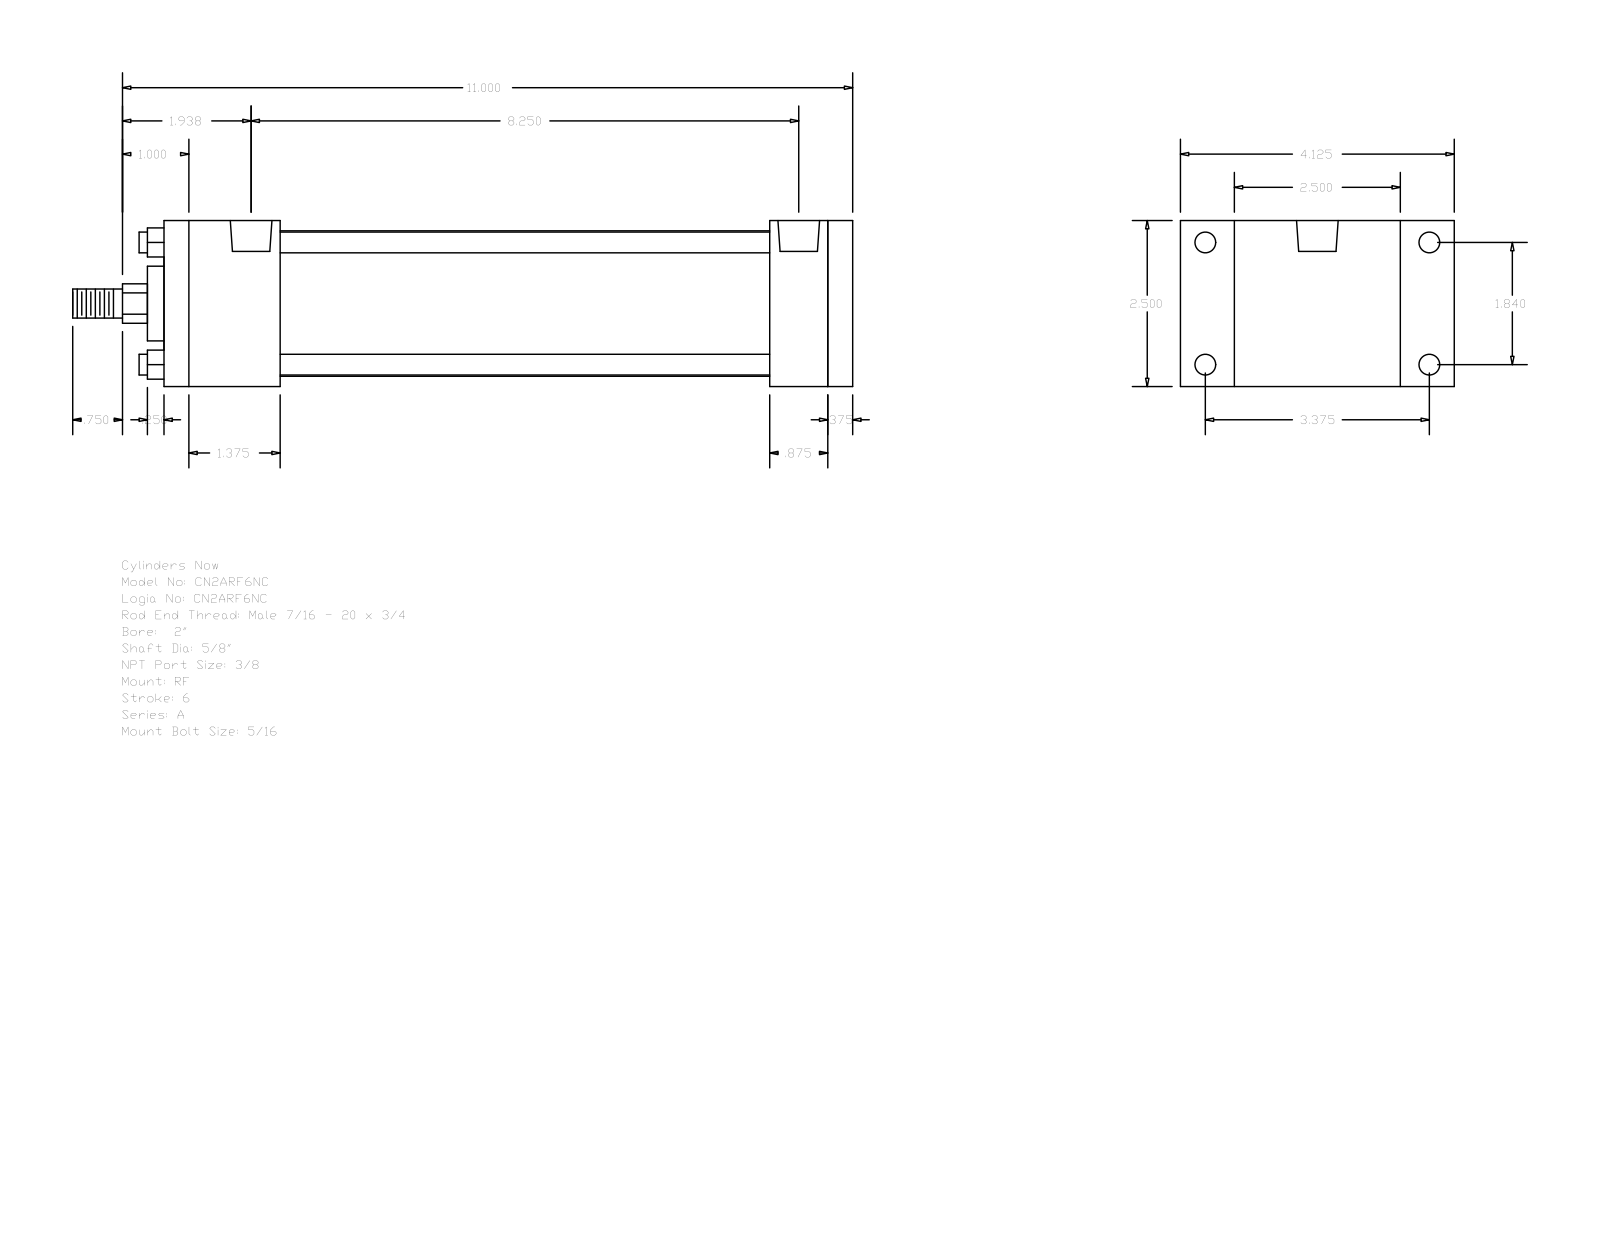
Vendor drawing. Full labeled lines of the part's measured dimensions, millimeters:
Part name (STEP PRODUCT): A_RF__0200_0.625
STEP written by: GSSL Pune (CONFIG_CONTROL_DESIGN)
Units: millimetres
Bodies: 0 solids, 92 faces (64 planar, 28 cylindrical, 0 other)
Overall size (bounding box): 298.45 × 104.78 × 63.5
Round holes (diameter × count): ⌀5.56 ×4, ⌀7.94 ×4, ⌀15.93 ×2
Round bosses / shafts (diameter × count): ⌀7.94 ×4, ⌀55.63 ×1, ⌀28.57 ×1, ⌀15.88 ×1, ⌀11.11 ×1
Partial cylindrical surfaces — rounded edges, fillets, slot ends (radius × count): R7.54 ×1
Main face-to-face distances: 63.5, 263.52, 254, 9.52, 44.45, 209.55, 219.07, 231.77, 187.32, 22.23
Hole centre spacings: 46.74, 85.72, 97.63, 201.6, 3.97, 3.98, 205.57, 205.58
